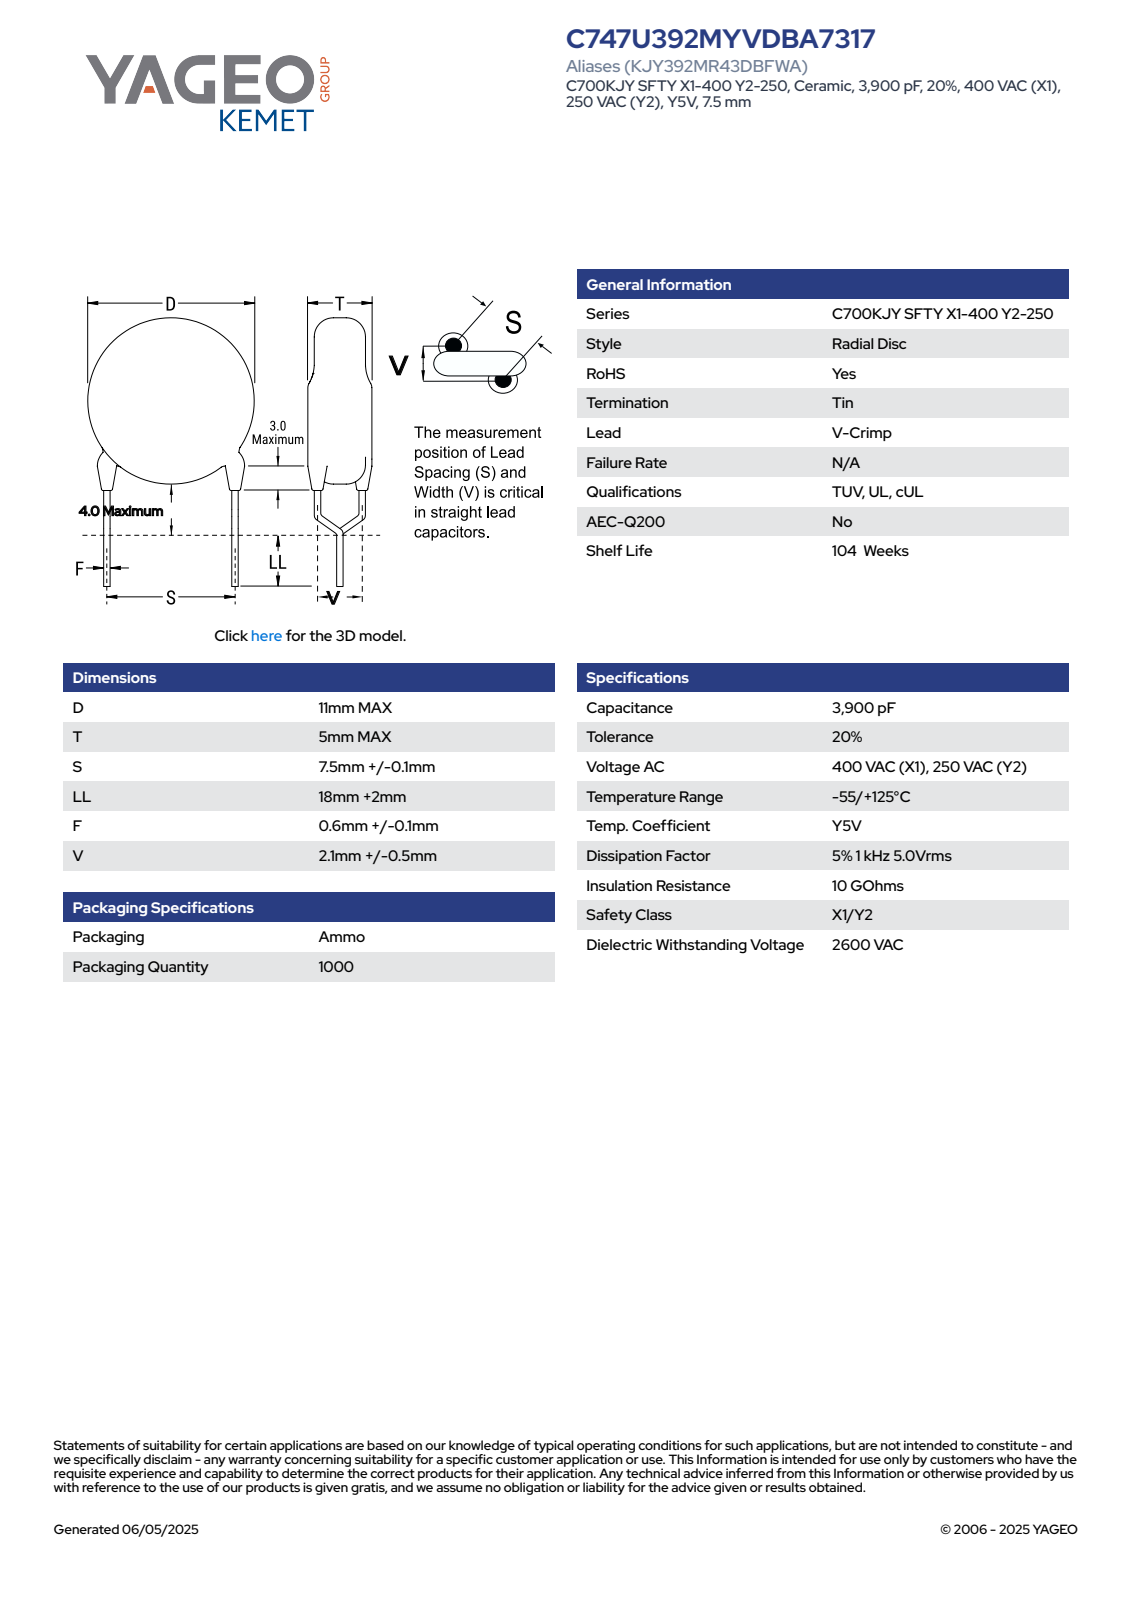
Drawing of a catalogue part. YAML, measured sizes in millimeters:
part_name: "CCD_VC11X5_D11T5S7.5LL20F0.7V2.1"
step_written_by: "SolidWorks 2021 (AUTOMOTIVE_DESIGN)"
units: millimeters
bodies: {solids: 4, faces: 85, planar: 63, cylindrical: 18, other: 4}
overall_size: [31, 11, 5]
volume: 480
surface_area: 439
round_bosses_or_shafts:
  - {diameter: 0.7, count: 6}
  - {diameter: 1.2, count: 2}
  - {diameter: 11, count: 1}
face_to_face_distances: [5, 20, 0.97, 26.01, 6.01, 25.04, 5.04, 0.42, 0.6, 3.96]
